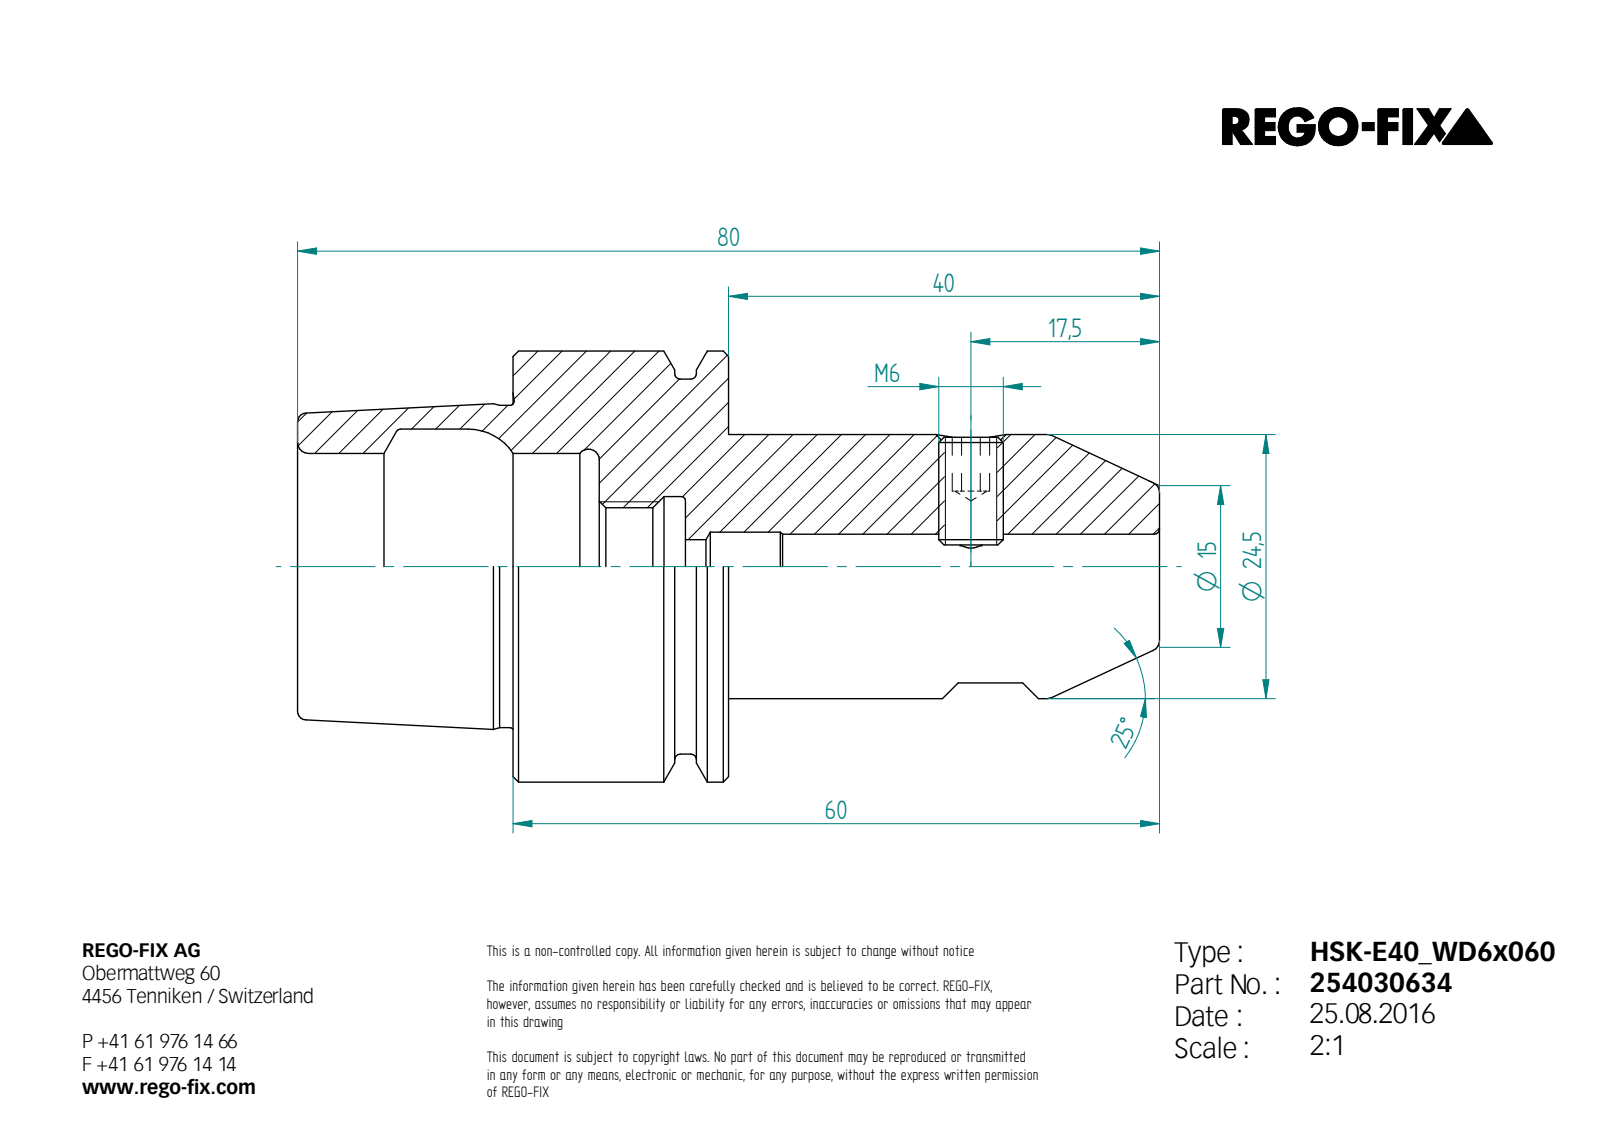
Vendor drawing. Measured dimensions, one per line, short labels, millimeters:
written by: Unknown (AUTOMOTIVE_DESIGN)
unit: mm
bodies: 2 solids, 69 faces (25 planar, 15 cylindrical, 29 other)
size: 80 × 40 × 40
volume: 41 530 mm³; area: 13 360 mm²
holes: 1× ⌀4.92, 1× ⌀5, 1× ⌀6, 1× ⌀6.4, 1× ⌀10.92, 1× ⌀13, 1× ⌀21, 1× ⌀25.5
bosses: 1× ⌀40, 1× ⌀34.8, 1× ⌀29.91, 1× ⌀24.5, 1× ⌀6
face distances: 20, 8, 40, 12, 28, 80, 60, 52, 36, 16
